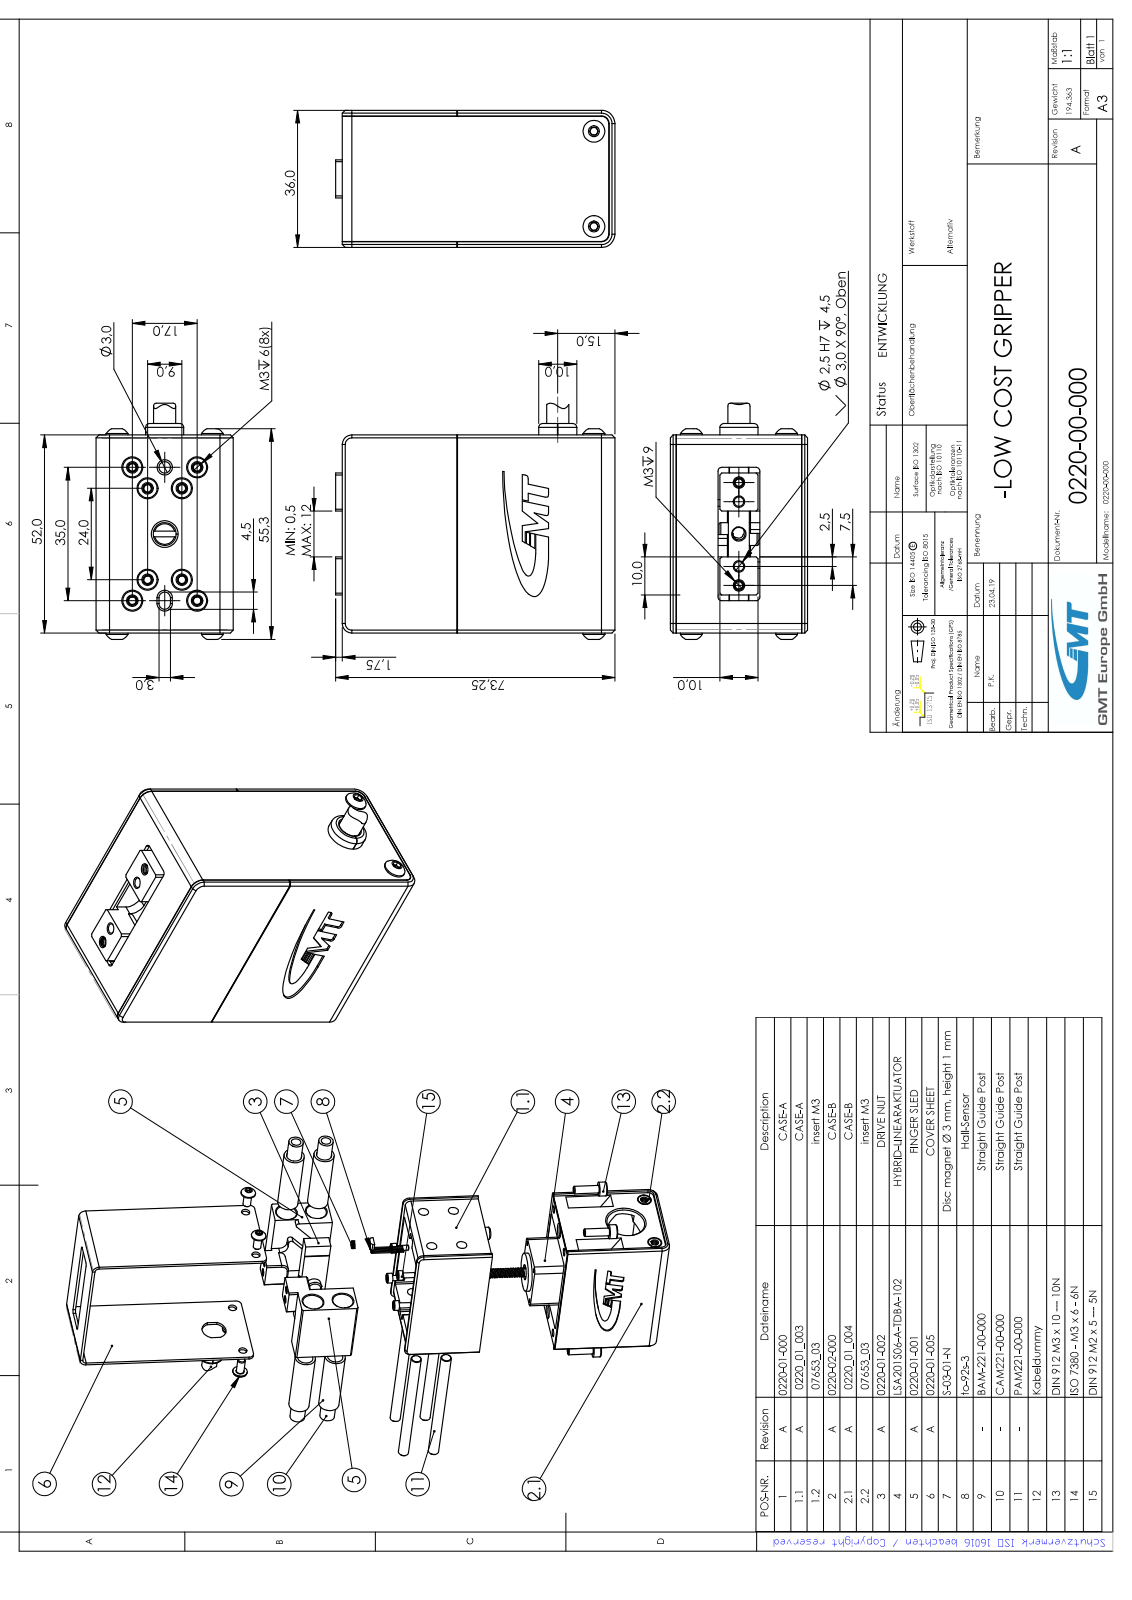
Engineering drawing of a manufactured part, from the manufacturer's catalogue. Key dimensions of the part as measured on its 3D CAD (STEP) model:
Part name (STEP PRODUCT): din 912 m2 x 5 --- 5n_DIN 912 M2 x 5 --- 5N; BAM-221-00-000; 07653_03; 0220_01_003 (+8 more)
STEP written by: SolidWorks 2018 (AUTOMOTIVE_DESIGN)
Units: millimetres
Bodies: 51 solids, 2514 faces (736 planar, 926 cylindrical, 852 other)
Overall size (bounding box): 73.25 × 62.01 × 36
Volume: 91 755 mm³ · Surface area: 72 938 mm²
Round holes (diameter × count): ⌀1.5 ×42, ⌀0.6 ×6, ⌀3 ×6, ⌀6 ×6, ⌀4 ×5, ⌀1.6 ×4, ⌀2.4 ×4, ⌀2.5 ×4, ⌀3.75 ×4, ⌀4.4 ×4, ⌀8 ×4, ⌀3.2 ×2
Round bosses / shafts (diameter × count): ⌀4.5 ×14, ⌀2.5 ×14, ⌀0.5 ×12, ⌀5.75 ×4, ⌀5.5 ×4, ⌀3.8 ×4, ⌀2 ×4, ⌀3 ×3
Partial cylindrical surfaces — rounded edges, fillets, slot ends (radius × count): R0.5 ×20, R1 ×16, R2 ×10, R1.5 ×4, R3 ×4, R2.5 ×2, R3.5 ×2, R0.3 ×1
Main face-to-face distances: 1, 2.5, 51, 36, 33.5, 50, 25, 8, 52, 6.5
Hole centre spacings: 4.5, 44, 1.5, 1.74, 2.76, 3, 6.76, 7.64
